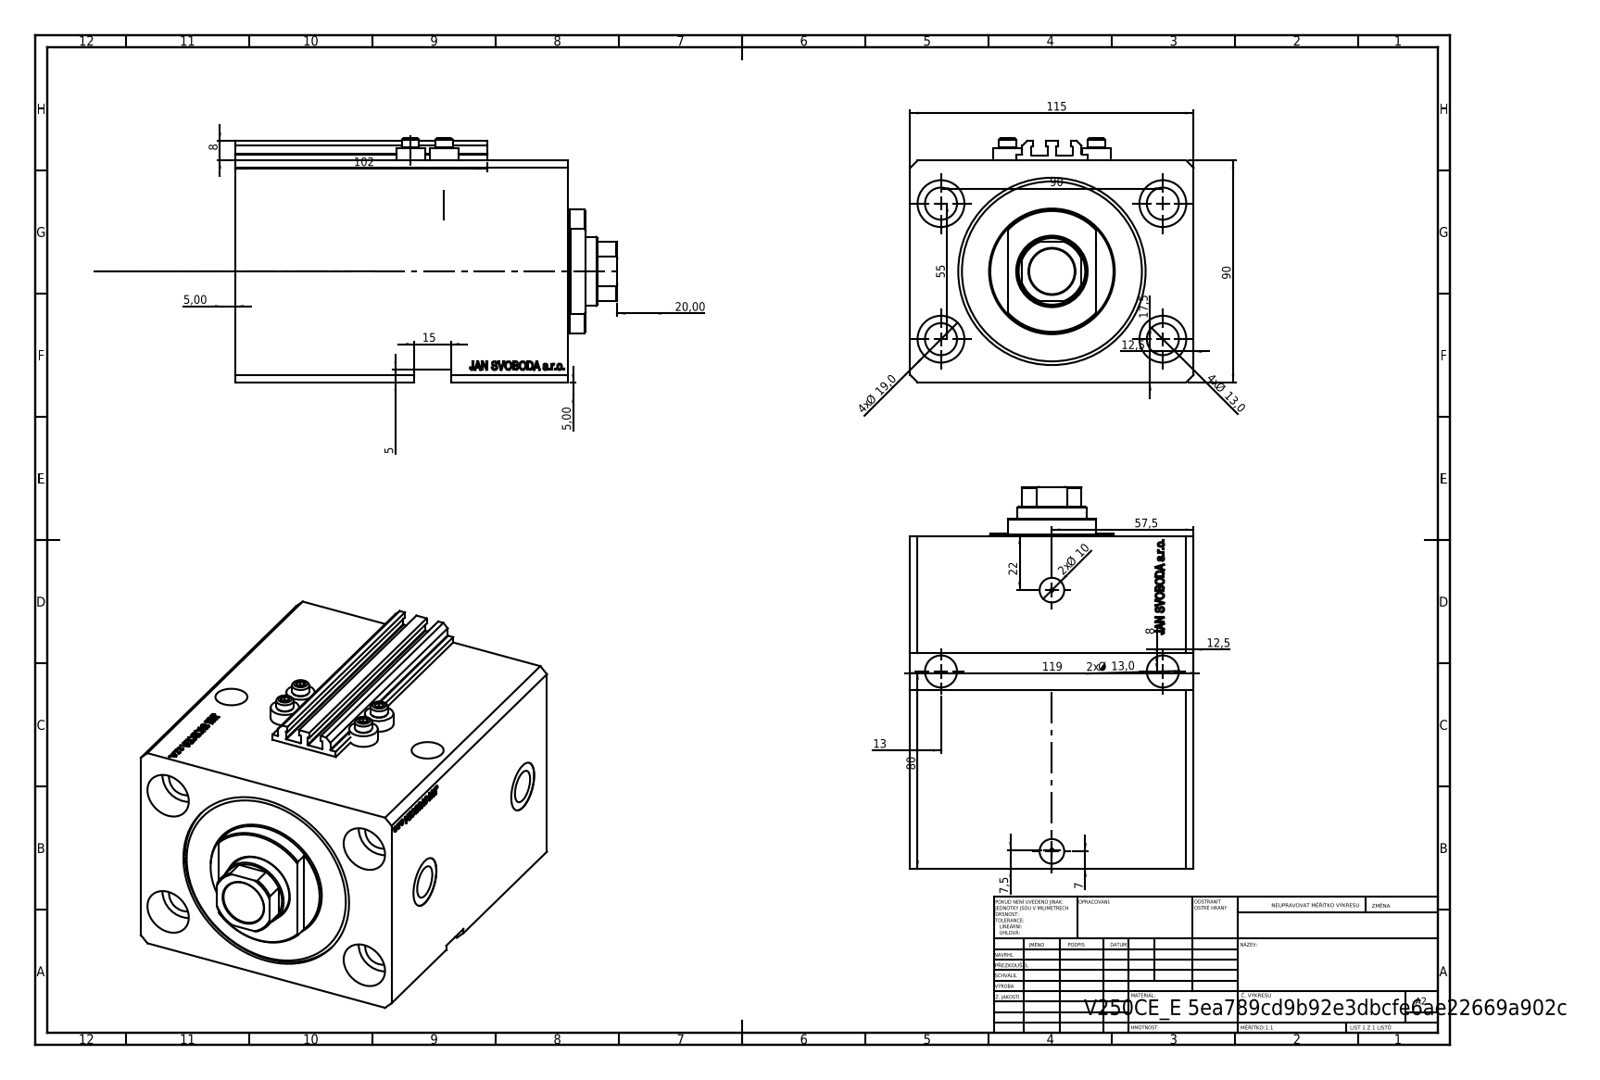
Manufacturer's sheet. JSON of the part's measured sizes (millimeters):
{"part_name": "V250CE_E_Body; ALLEN BOLT V250CE; V250CE_VC_E; V250CE_C_VCP", "step_written_by": "SolidWorks 2019 (CONFIG_CONTROL_DESIGN)", "units": "millimeters", "bodies": {"solids": 8, "faces": 1107, "planar": 543, "cylindrical": 126, "other": 438}, "overall_size": [154.9, 115, 99], "volume_mm3": 1177000, "surface_area_mm2": 185082, "round_holes": [[13, 6], [1.25, 4], [4, 4], [19, 4], [10, 2], [13.16, 2], [20, 2], [18.5, 1], [28, 1], [63, 1], [76, 1]], "round_bosses_or_shafts": [[11.6, 4], [7, 4], [50, 1]], "partial_cylinders_radius": [[0.2, 10], [13.5, 1]], "face_to_face_distances": [90, 115, 135, 87, 17.9, 117.1, 104.9, 30.1, 50, 54.9], "hole_center_spacings": [52.74, 90, 13.6, 27.39, 28.46, 33.62, 36, 38.48]}
